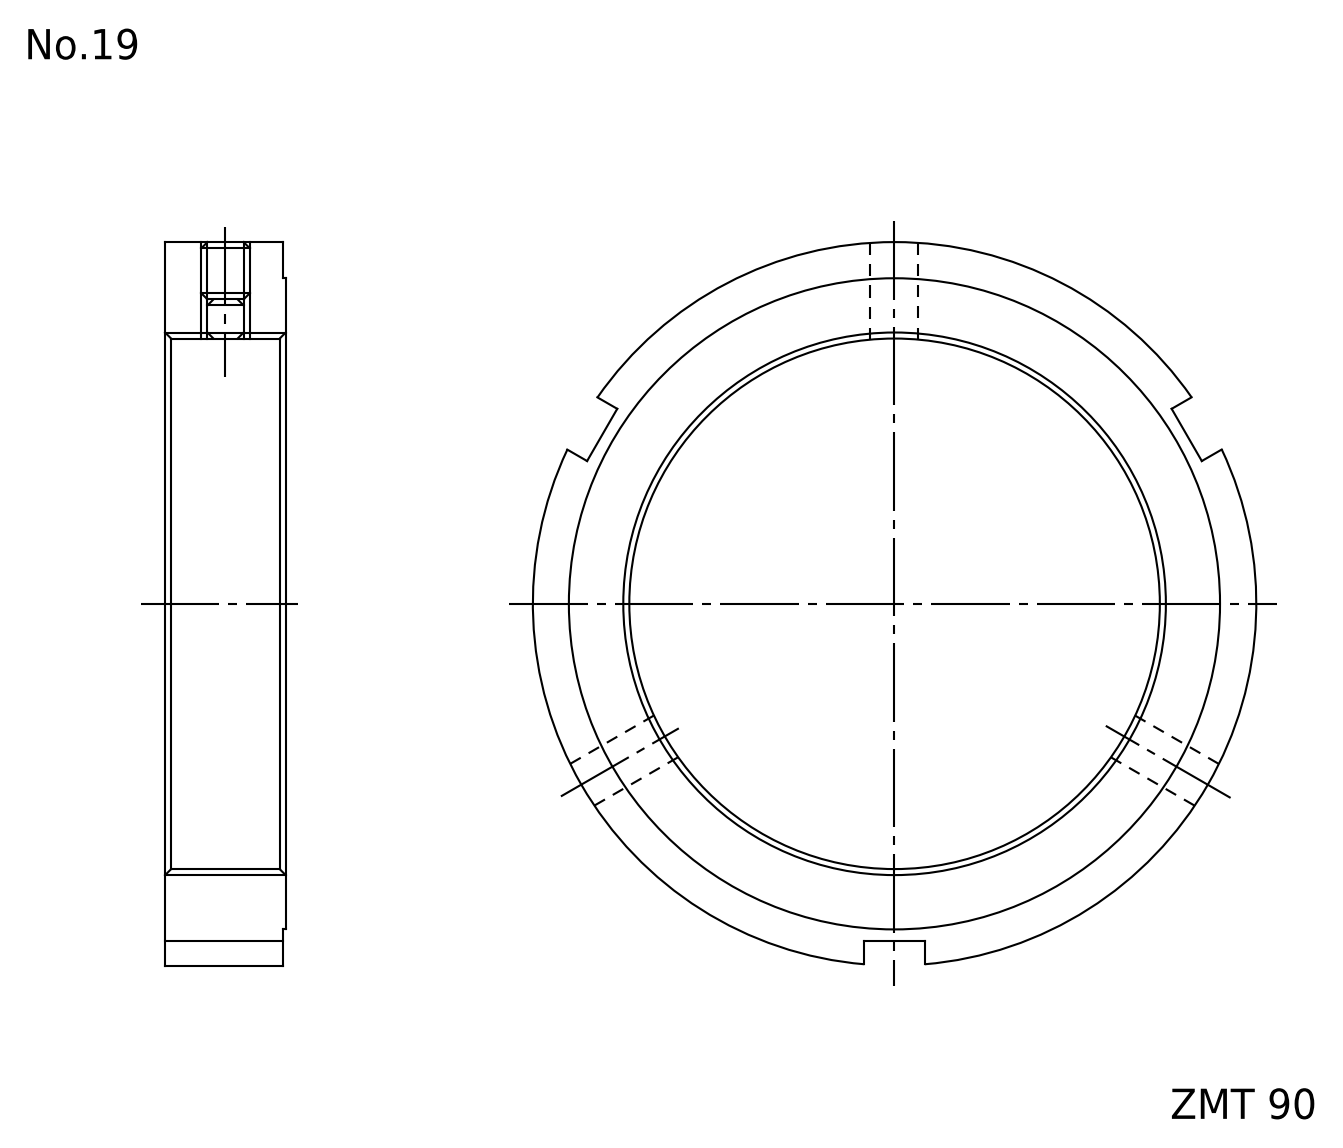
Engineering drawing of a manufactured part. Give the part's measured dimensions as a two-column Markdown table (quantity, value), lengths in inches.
| quantity | value |
| --- | --- |
| part name | FKD ZMT 90 |
| STEP written by | Autodesk Inventor 2011 (AUTOMOTIVE_DESIGN) |
| units | inches |
| bodies | 1 solid, 20 faces (12 planar, 8 cylindrical, 0 other) |
| overall size | 4.724 × 4.716 × 0.787 |
| volume | 5.738 in³ |
| surface area | 37.22 in² |
| round holes (diameter × count) | 0.262 × 3, 3.543 × 1 |
| round bosses / shafts (diameter × count) | 4.724 × 1, 4.252 × 1 |
| main face-to-face distances | 0.787, 0.02, 0.768, 0.394 |
